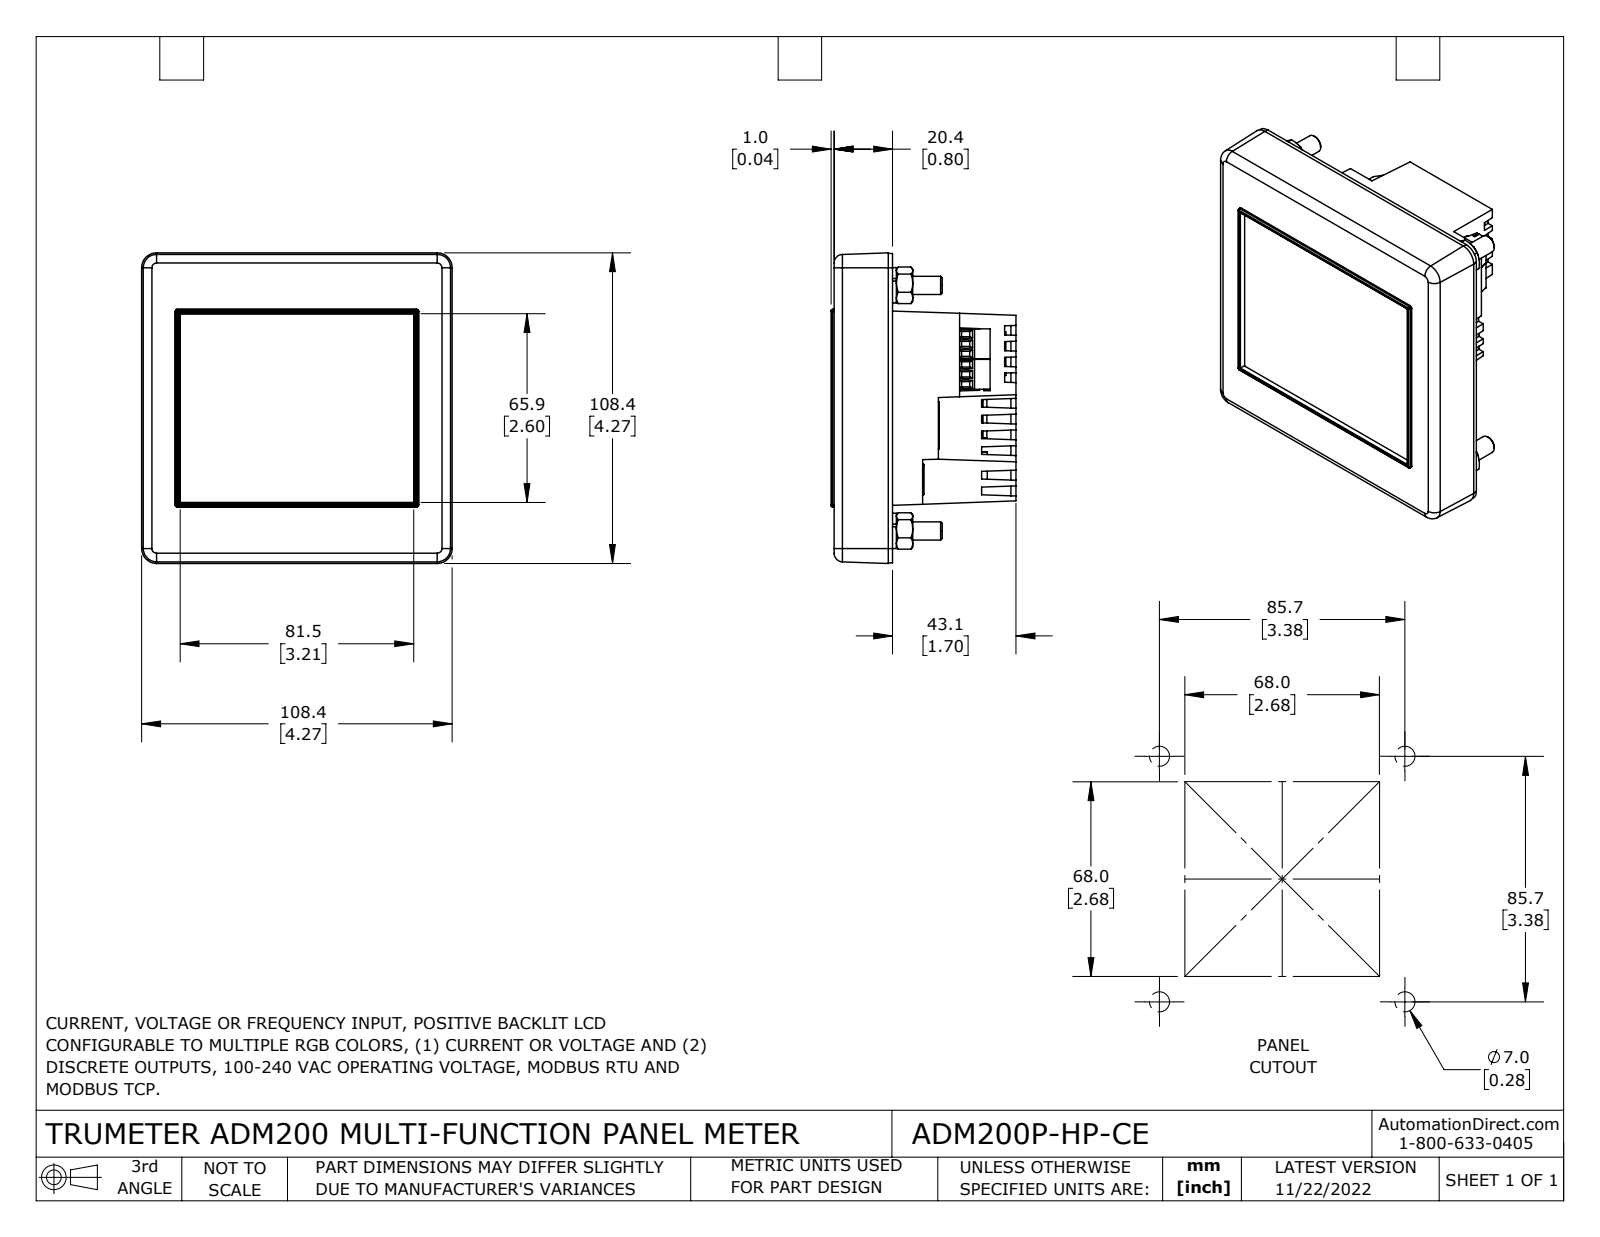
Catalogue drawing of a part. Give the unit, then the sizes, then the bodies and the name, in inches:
Units: inches
Overall size (bounding box): 4.269 × 4.269 × 2.541
Round holes (diameter × count): ⌀0.071 ×9, ⌀0.114 ×6, ⌀0.118 ×5, ⌀0.213 ×4, ⌀0.25 ×4, ⌀0.26 ×4, ⌀0.295 ×4, ⌀0.154 ×2
Round bosses / shafts (diameter × count): ⌀0.039 ×5, ⌀0.487 ×4, ⌀0.438 ×4, ⌀0.024 ×4, ⌀0.079 ×2
Partial cylindrical surfaces — rounded edges, fillets, slot ends (radius × count): R0.006 ×32, R0.02 ×30, R0.039 ×7, R0.016 ×4, R0.03 ×4, R0.118 ×4, R0.197 ×4, R0.004 ×2
Main face-to-face distances: 0.031, 0.635, 0.11, 0.073, 0.059, 0.079, 0.694, 3.395, 3.468, 0.047
Hole centre spacings: 0.709, 3.228, 0.136, 0.293, 0.986, 1.417, 2.126, 2.399
Volume: 7.808 in³ · Surface area: 190.8 in²
Bodies: 23 solids, 2059 faces (1384 planar, 290 cylindrical, 385 other)
Part name (STEP PRODUCT): ADM200P-HP-CE
STEP written by: SolidWorks 2021 (CONFIG_CONTROL_DESIGN)
